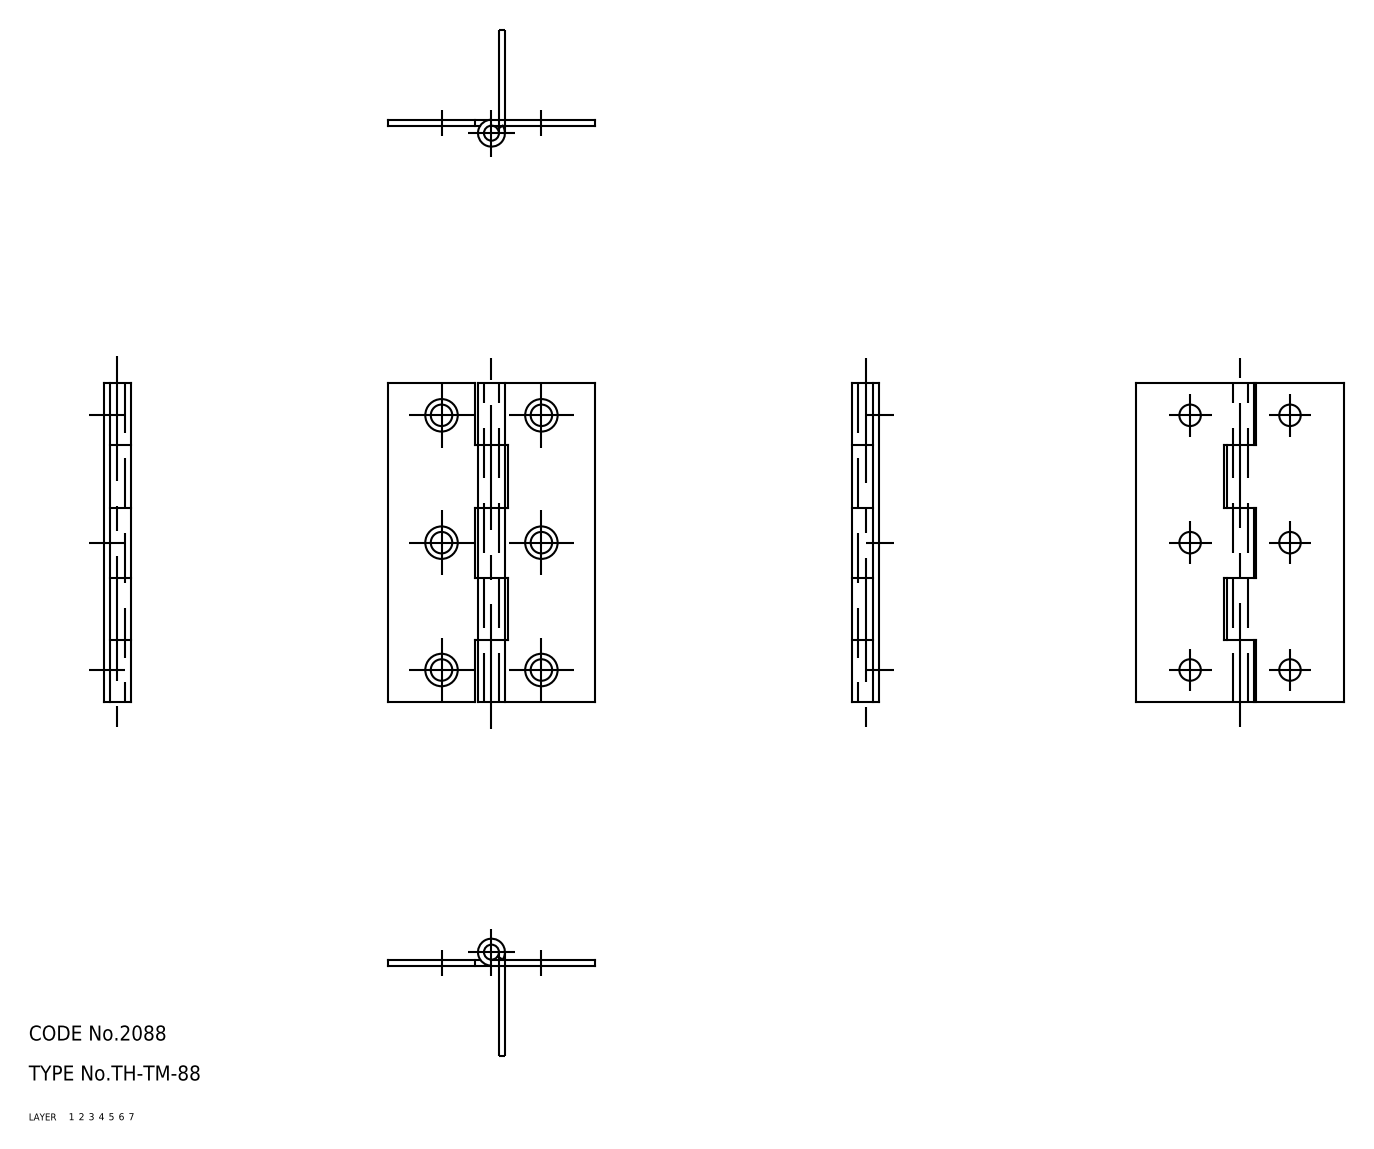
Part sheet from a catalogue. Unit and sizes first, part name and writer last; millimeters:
Units: millimetres
Overall size (bounding box): 64 × 41.5 × 5.4
Volume: 4 080 mm³ · Surface area: 7 377 mm²
Bodies: 3 solids, 66 faces (0 planar, 0 cylindrical, 66 other)
Part name (STEP PRODUCT): shaft; hinge piece_B; hinge piece_A; TH_TM_88_26461_36
STEP written by: CADfix (AUTOMOTIVE_DESIGN)
